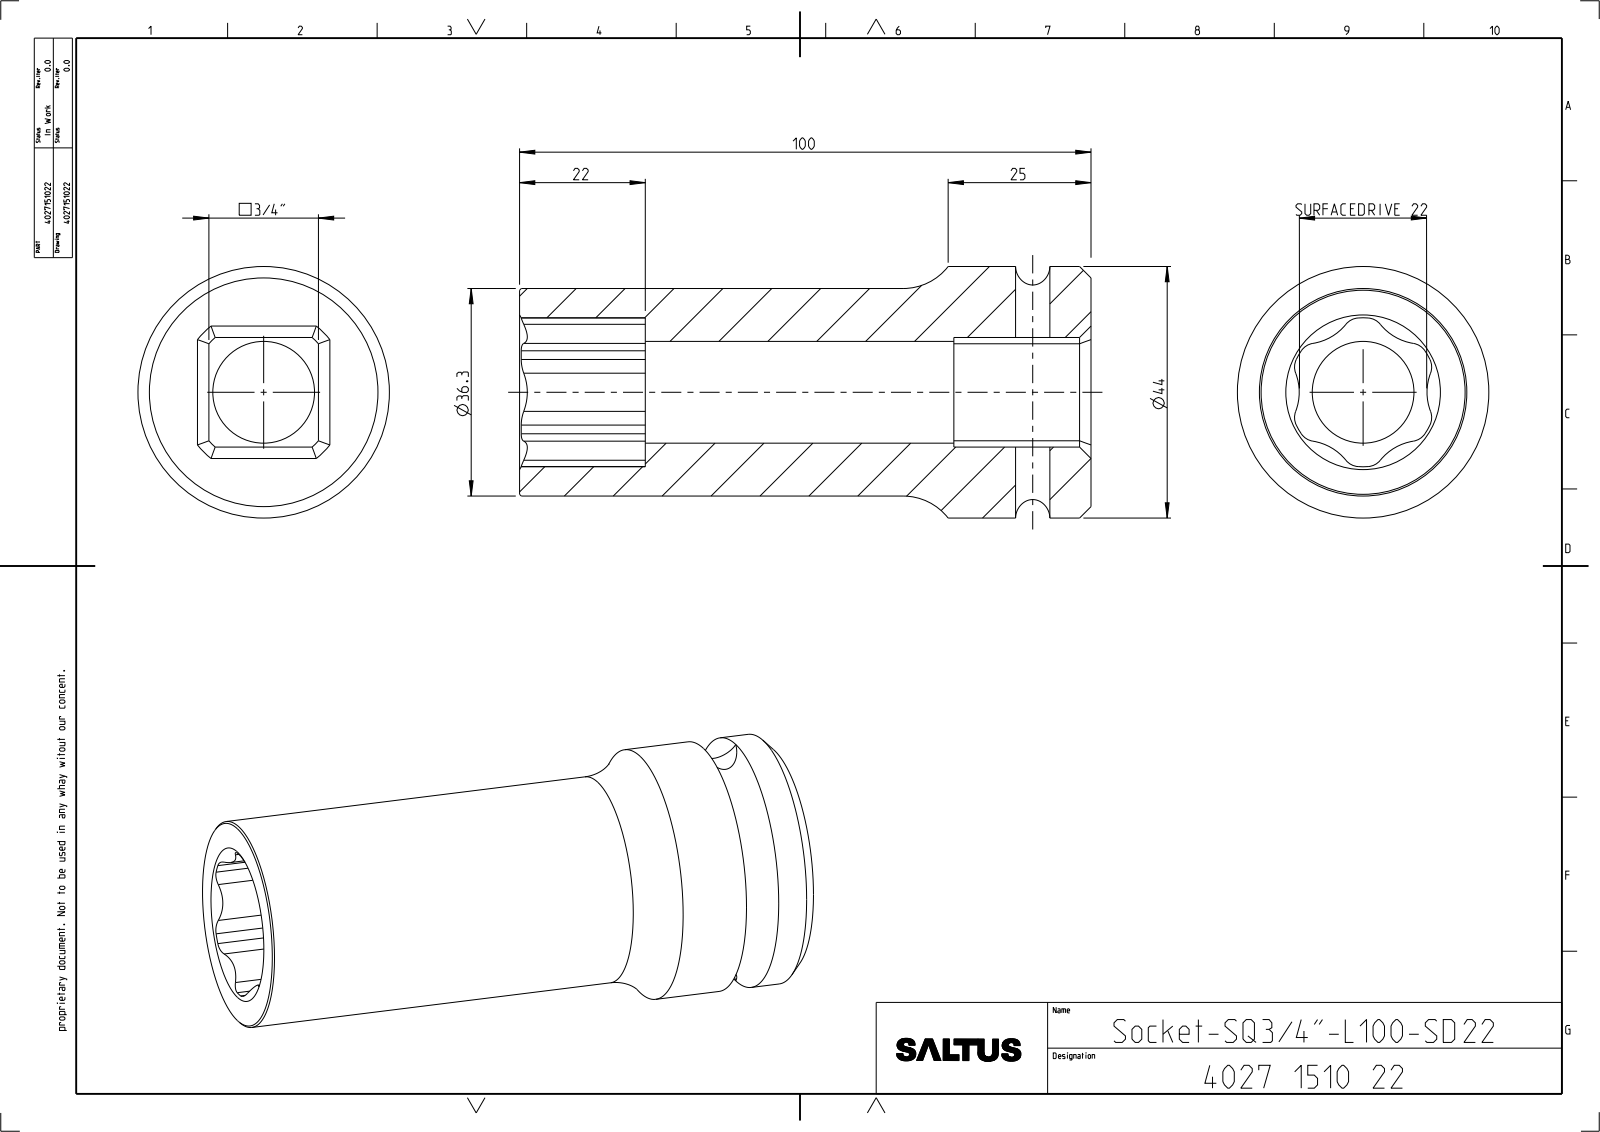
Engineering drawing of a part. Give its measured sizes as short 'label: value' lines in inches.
name: 4027151022
written by: CREO PARAMETRIC BY PTC INC, 2022414 (CONFIG_CONTROL_DESIGN)
unit: in
bodies: 1 solid, 66 faces (12 planar, 40 cylindrical, 14 other)
size: 3.937 × 1.732 × 1.732
volume: 4.969 in³; area: 32.82 in²
holes: 1× ⌀0.236, 1× ⌀0.701
bosses: 1× ⌀1.732, 1× ⌀1.429
rounds: 12× R0.118, 6× R0.366, 1× R0.504, 1× R0.513
face distances: 0.755, 3.937, 3.071, 0.866, 0.945, 2.126, 2.992
